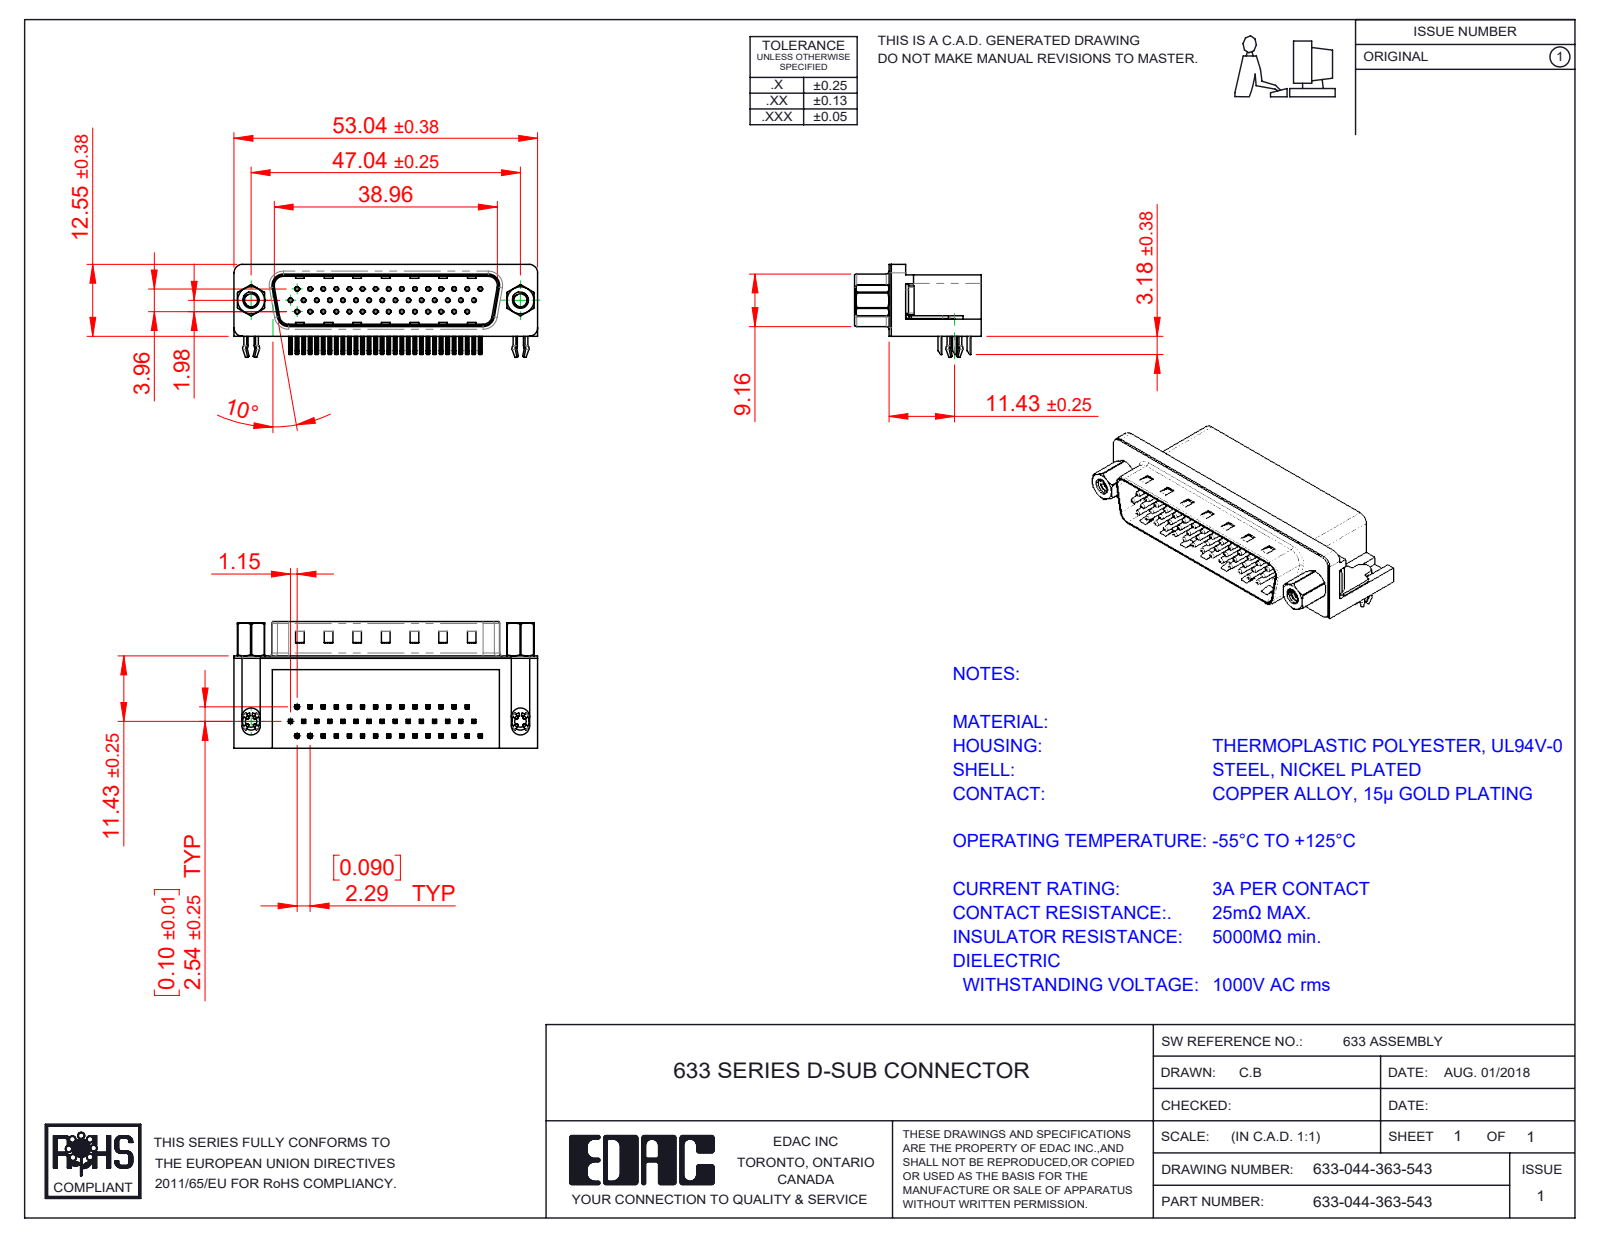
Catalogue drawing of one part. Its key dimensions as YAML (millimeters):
part_name: "633 4 Prong Board Lock; 633 4-40 Hex Standoff; 633 Shell_44 Contact; 633 Housing_44 Contact (+5 more)"
step_written_by: "SolidWorks 2016 (CONFIG_CONTROL_DESIGN)"
units: millimeters
bodies: {solids: 52, faces: 3930, planar: 2381, cylindrical: 1130, other: 419}
overall_size: [53.04, 22.1, 16.25]
volume: 8326
surface_area: 10746
round_holes:
  - {diameter: 0.35, count: 44}
  - {diameter: 0.8, count: 44}
  - {diameter: 2, count: 2}
  - {diameter: 2.26, count: 2}
  - {diameter: 2.29, count: 2}
  - {diameter: 4, count: 2}
  - {diameter: 4.8, count: 2}
  - {diameter: 5, count: 2}
round_bosses_or_shafts:
  - {diameter: 0.75, count: 44}
  - {diameter: 4.9, count: 2}
  - {diameter: 4.75, count: 2}
  - {diameter: 3.9, count: 2}
  - {diameter: 3, count: 2}
  - {diameter: 2.79, count: 2}
partial_cylinders:
  - {radius: 0.25, count: 188}
  - {radius: 0.12, count: 88}
  - {radius: 1, count: 16}
  - {radius: 0.5, count: 9}
  - {radius: 1.6, count: 8}
  - {radius: 1.5, count: 7}
  - {radius: 0.9, count: 4}
  - {radius: 2, count: 4}
face_to_face_distances: [0.4, 10.35, 15.7, 8.76, 2.9, 2.5, 16.1, 2.1, 10.7, 2.54]
hole_center_spacings: [2.29, 4.57, 4.58, 2.28, 6.87, 9.16, 11.45, 2.27]
